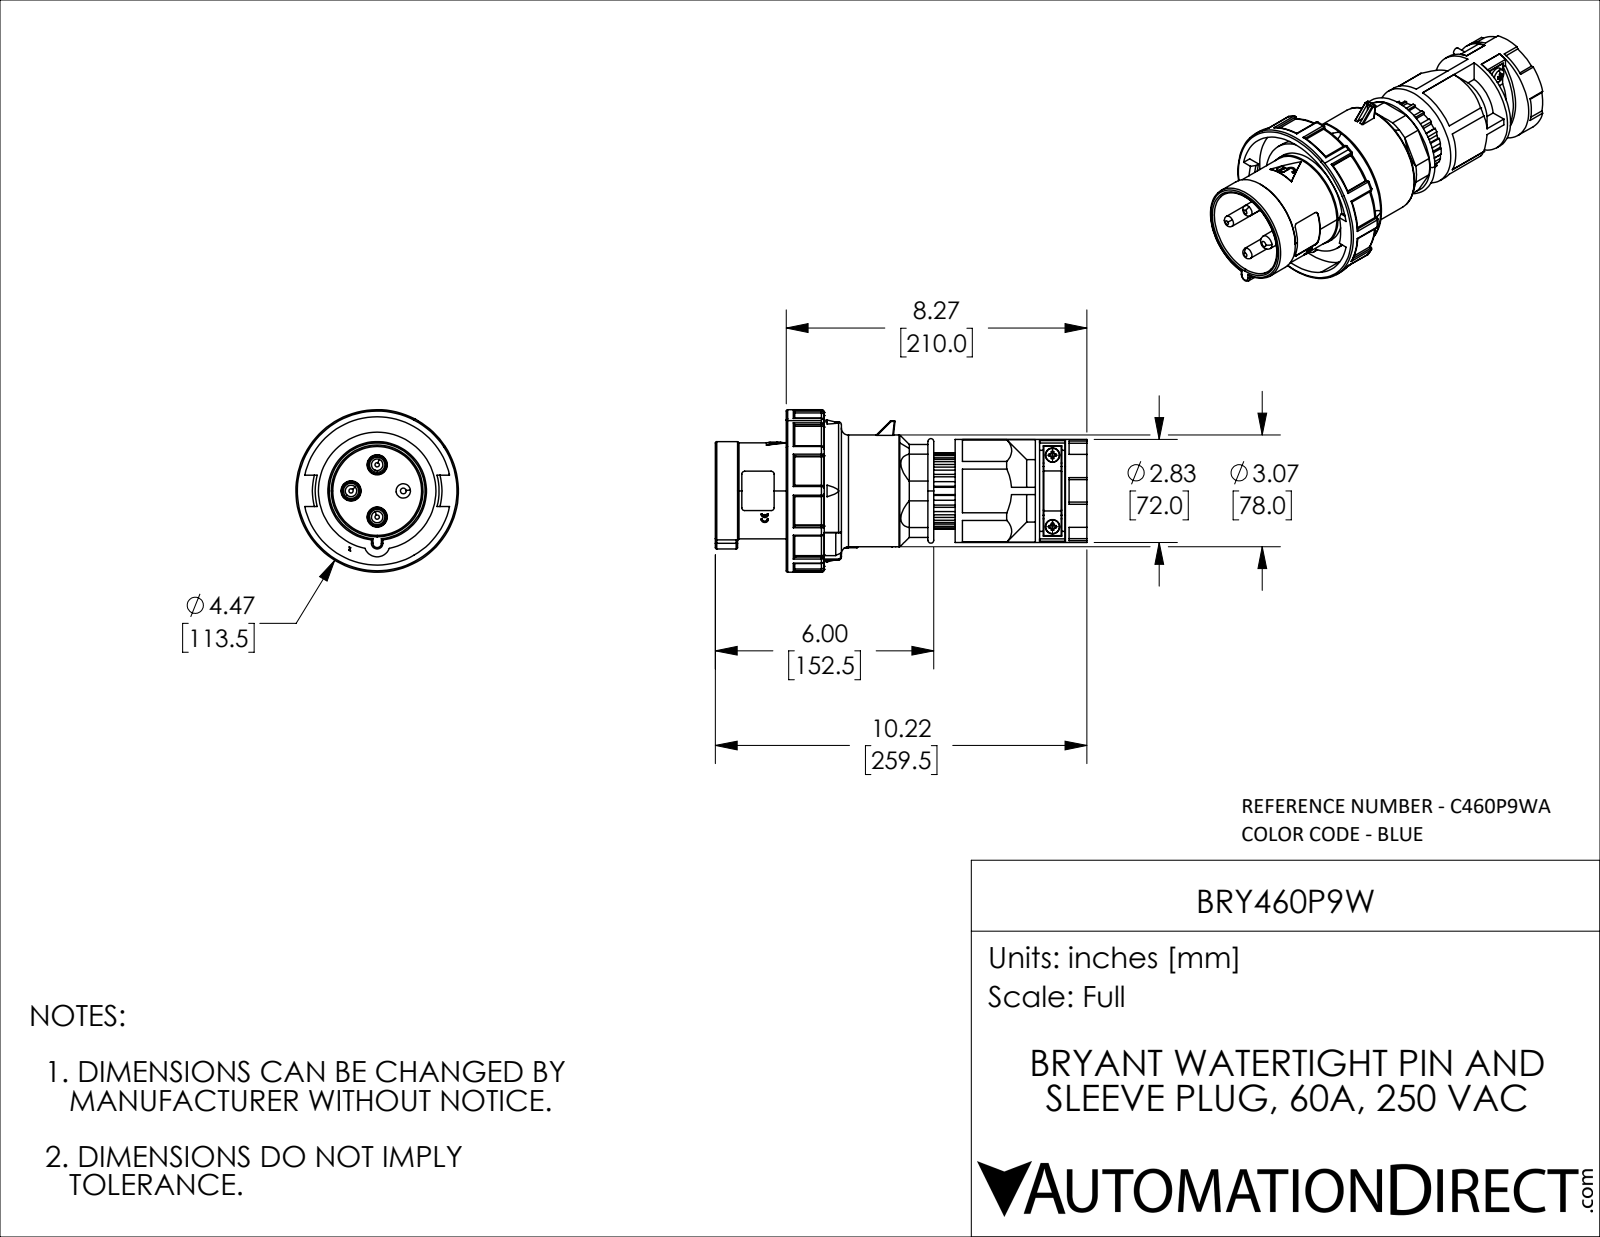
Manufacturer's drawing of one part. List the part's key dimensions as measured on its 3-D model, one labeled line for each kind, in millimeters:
Part name (STEP PRODUCT): BRY460P9W
STEP written by: SolidWorks 2021 (CONFIG_CONTROL_DESIGN)
Units: millimetres
Bodies: 8 solids, 1246 faces (489 planar, 422 cylindrical, 335 other)
Overall size (bounding box): 259.5 × 113.5 × 113.5
Volume: 754 113 mm³ · Surface area: 155 438 mm²
Round holes (diameter × count): ⌀2 ×2, ⌀5 ×2, ⌀37 ×1, ⌀62 ×1, ⌀65.5 ×1, ⌀103.5 ×1
Round bosses / shafts (diameter × count): ⌀8 ×3, ⌀113.5 ×1, ⌀105.34 ×1, ⌀82 ×1, ⌀78 ×1, ⌀72 ×1, ⌀68.9 ×1, ⌀68.03 ×1
Partial cylindrical surfaces — rounded edges, fillets, slot ends (radius × count): R1 ×39, R0.5 ×24, R2 ×18, R34.5 ×6, R0.4 ×4, R3 ×3, R4 ×3, R0.2 ×2
Main face-to-face distances: 86, 74, 160, 65, 15, 92, 5, 18, 3, 97
Hole centre spacings: 50
